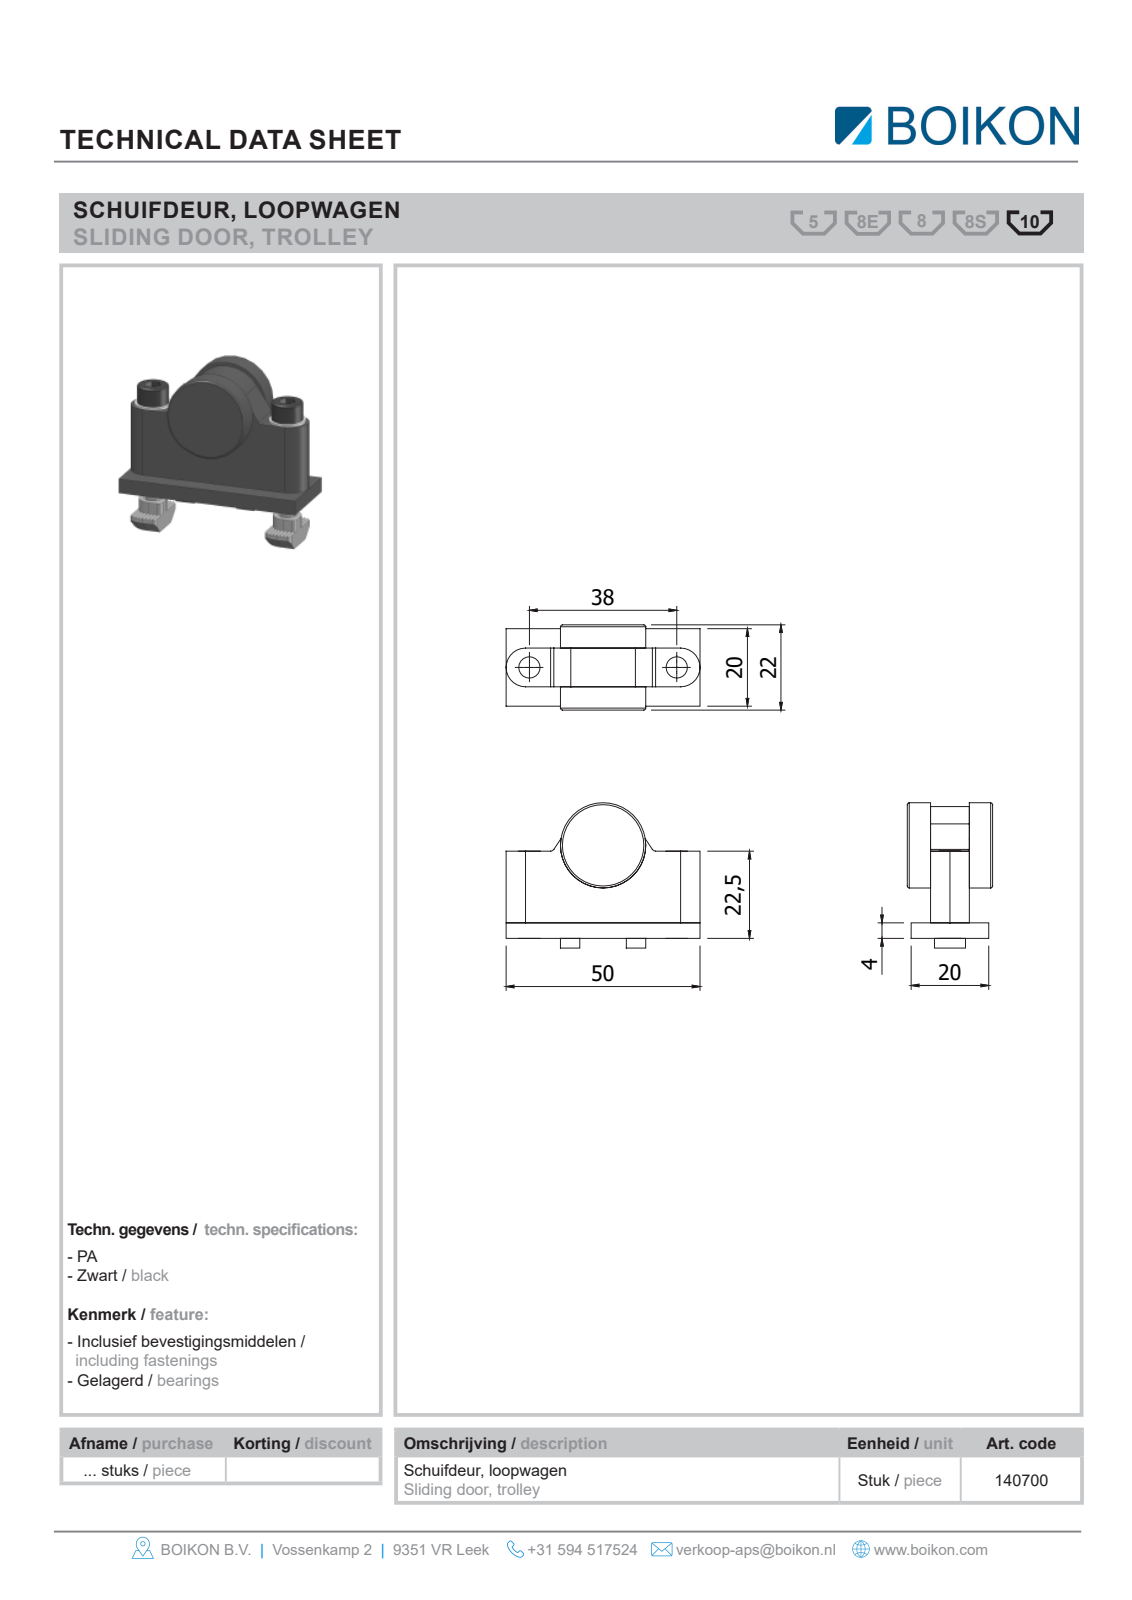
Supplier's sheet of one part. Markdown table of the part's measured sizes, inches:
| quantity | value |
| --- | --- |
| part name | Root; 140700Schuifdeur loopwagenBOIKON; 901904Kartelring DIN 6798A EV M5BOIKON0; 122320Sleufmoer 8 - M5 met kogelBOIKON (+1 more) |
| STEP written by | HiCAD 2013 1802.4 Build 509 (AUTOMOTIVE_DESIGN) |
| units | inches |
| bodies | 7 solids, 126 faces (83 planar, 33 cylindrical, 10 other) |
| overall size | 2.047 × 1.846 × 0.866 |
| volume | 1.39 in³ |
| surface area | 16.38 in² |
| round holes (diameter × count) | 0.197 × 2, 0.209 × 2, 0.217 × 2 |
| round bosses / shafts (diameter × count) | 0.394 × 2, 0.335 × 2, 0.158 × 2, 0.866 × 1 |
| partial cylindrical surfaces (radius × count) | 0.197 × 3, 0.02 × 2, 0.039 × 2, 0.079 × 2, 0.394 × 1 |
| main face-to-face distances | 0.236, 0.63, 0.394, 0.039, 0.157, 0.197, 0.866, 0.591, 0.827, 0.165 |
| hole center spacings | 1.496 |
